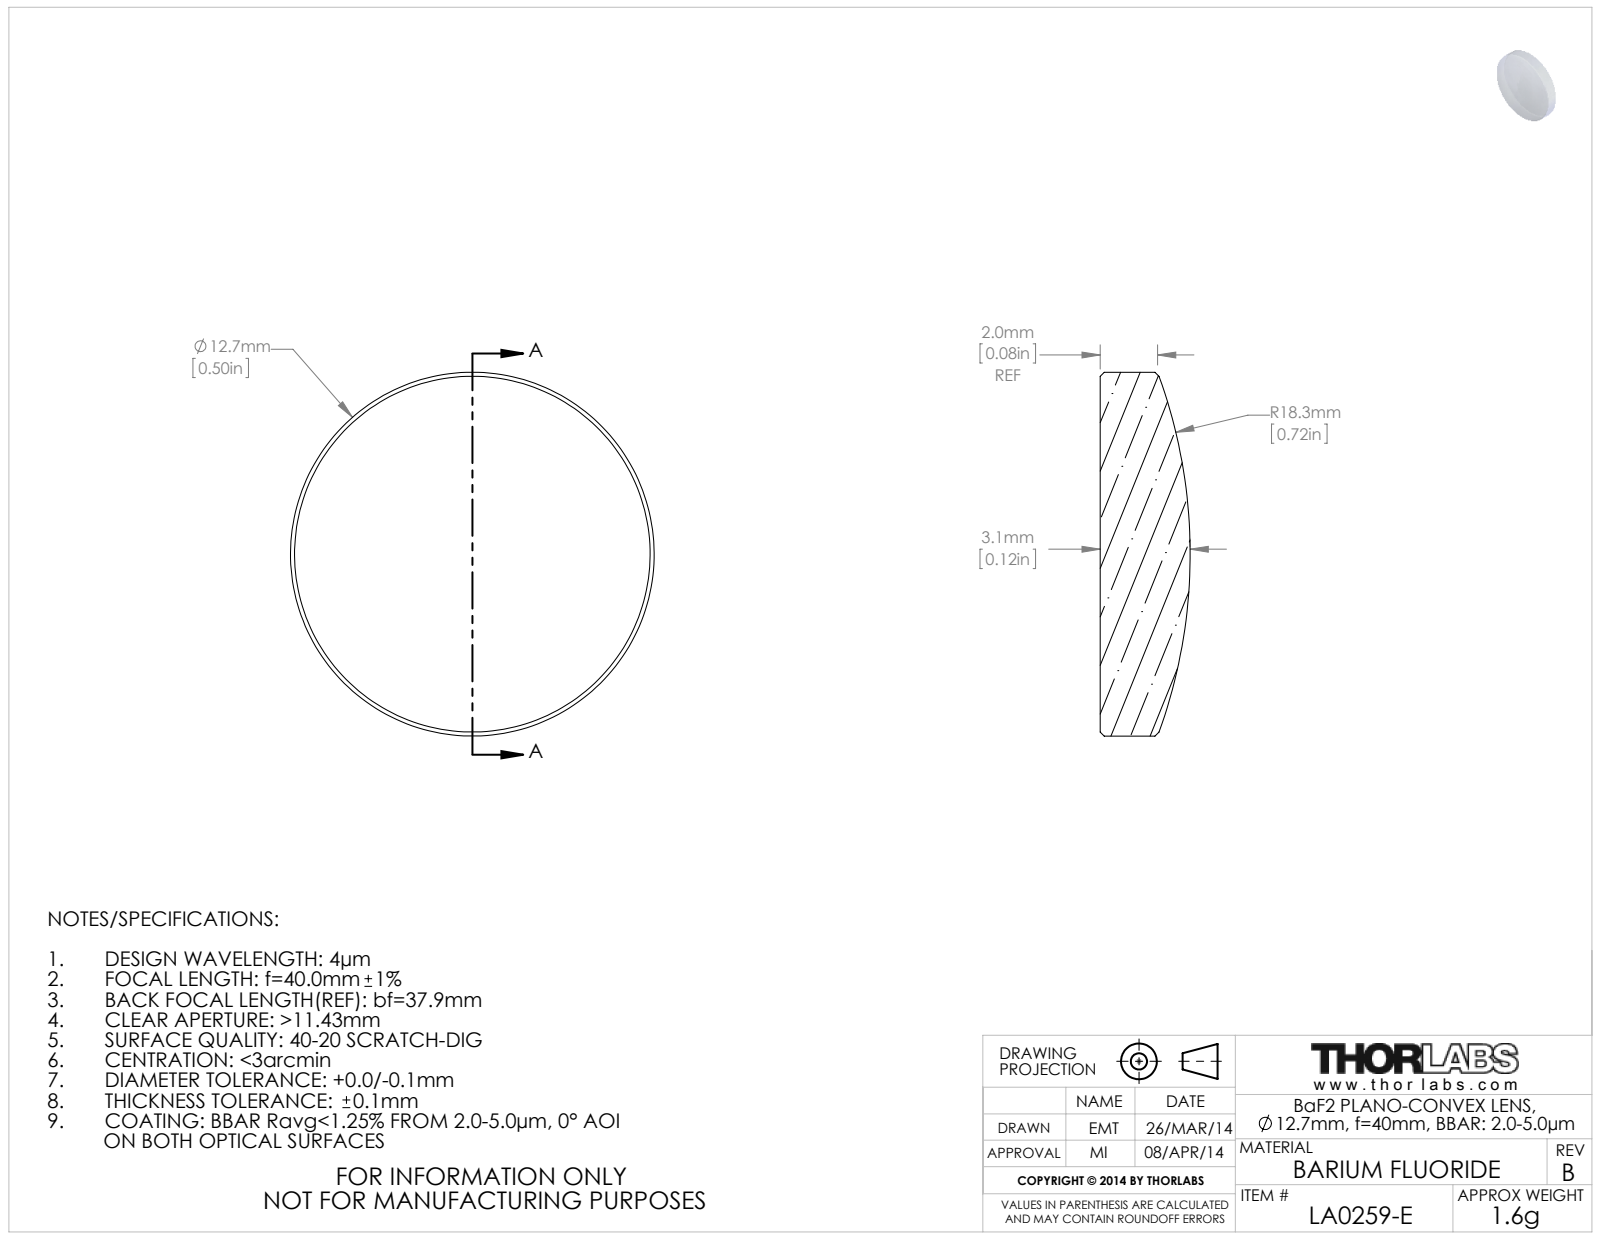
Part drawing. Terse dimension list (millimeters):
name: 20102-E0W
written by: SolidWorks 2014 (CONFIG_CONTROL_DESIGN)
unit: mm
bodies: 1 solid, 9 faces (1 planar, 2 cylindrical, 6 other)
size: 12.7 × 12.7 × 3.14
volume: 326 mm³; area: 332 mm²
bosses: 1× ⌀12.7
